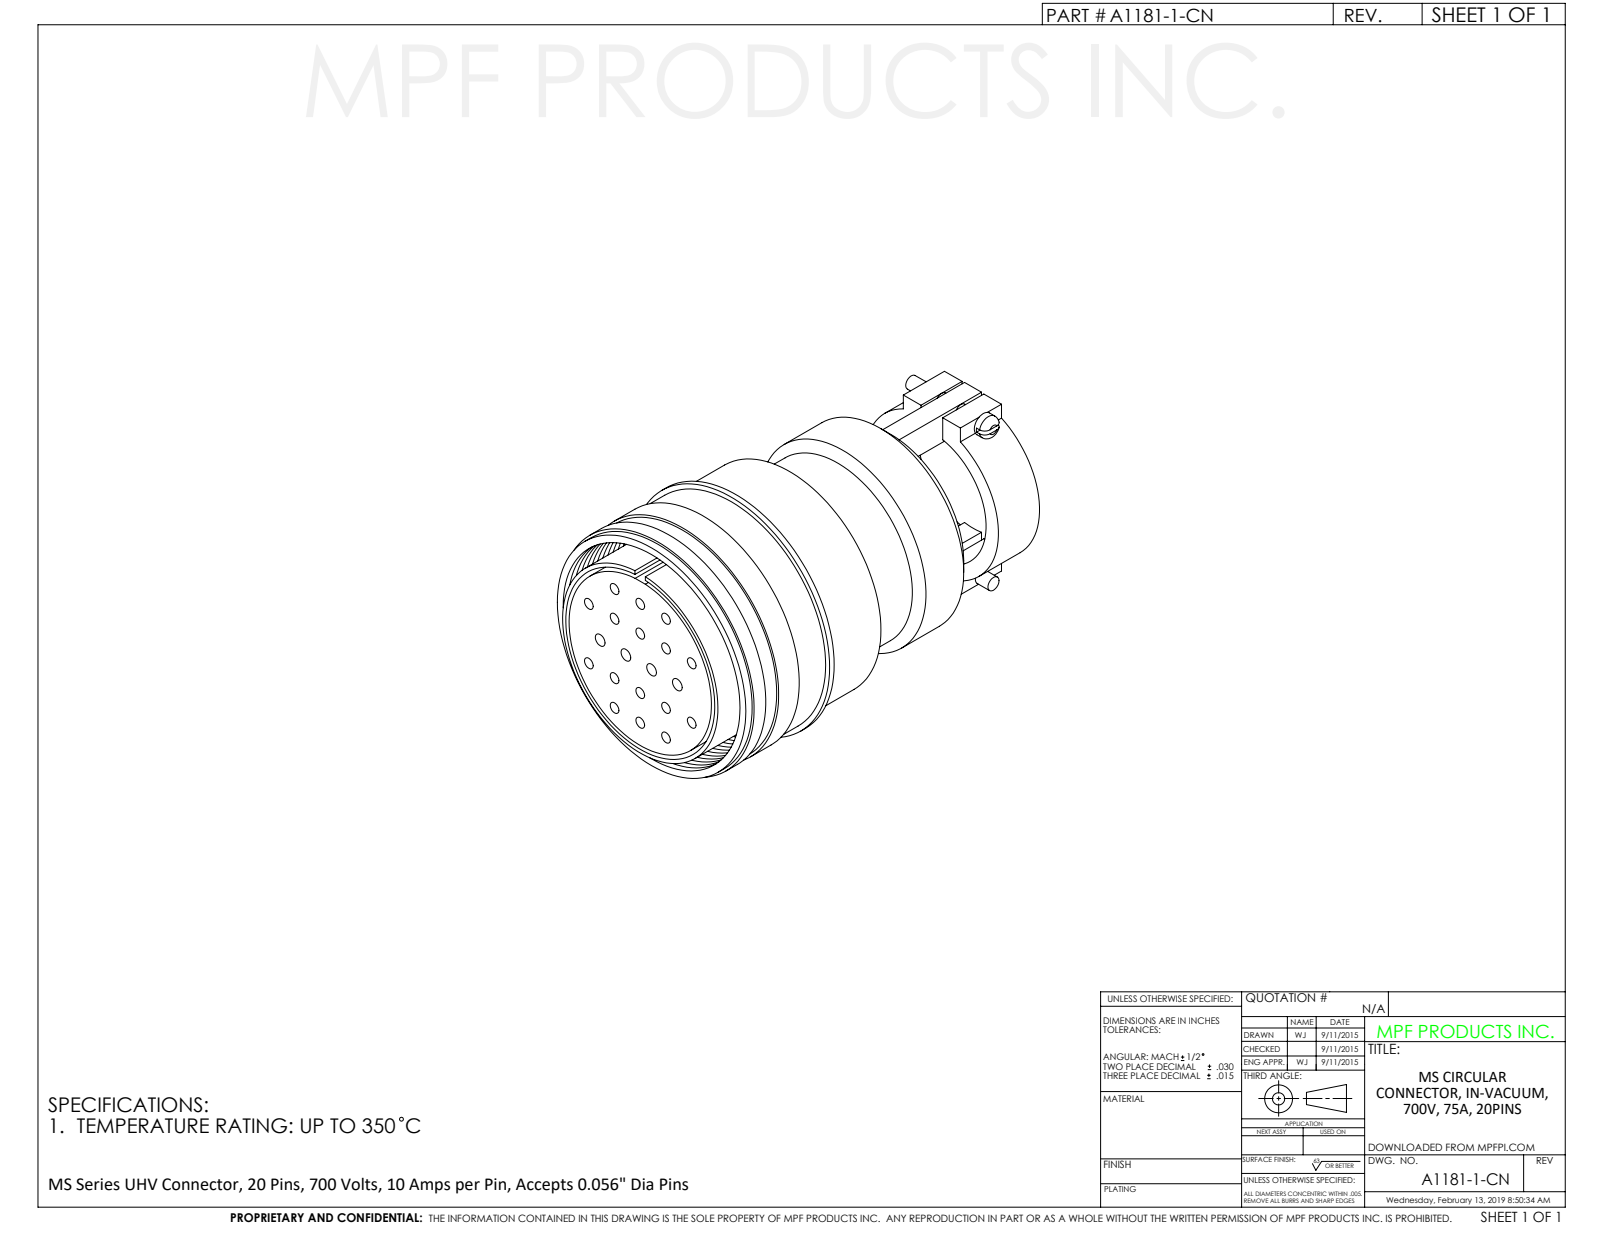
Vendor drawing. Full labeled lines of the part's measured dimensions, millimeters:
Part name (STEP PRODUCT): A1181-1-CN
STEP written by: SolidWorks 2012 (CONFIG_CONTROL_DESIGN)
Units: millimetres
Bodies: 1 solid, 390 faces (143 planar, 109 cylindrical, 138 other)
Overall size (bounding box): 74 × 47.8 × 47.8
Volume: 89 650 mm³ · Surface area: 28 660 mm²
Round holes (diameter × count): ⌀2.2 ×20, ⌀35.3 ×1, ⌀43.2 ×1
Round bosses / shafts (diameter × count): ⌀47.2 ×1, ⌀46.1 ×1, ⌀45 ×1, ⌀42.5 ×1, ⌀41.3 ×1, ⌀40.5 ×1, ⌀38.4 ×1, ⌀36.8 ×1
Partial cylindrical surfaces — rounded edges, fillets, slot ends (radius × count): R4.4 ×4, R11.4 ×1, R16.8 ×1
Main face-to-face distances: 72.9, 14.2, 58.6, 22.5, 36.8, 36.1, 50.4, 36.2, 13.6, 22.5
Hole centre spacings: 5.5, 17, 11.5, 5.6, 5.7, 6.3, 6.4, 7.8
